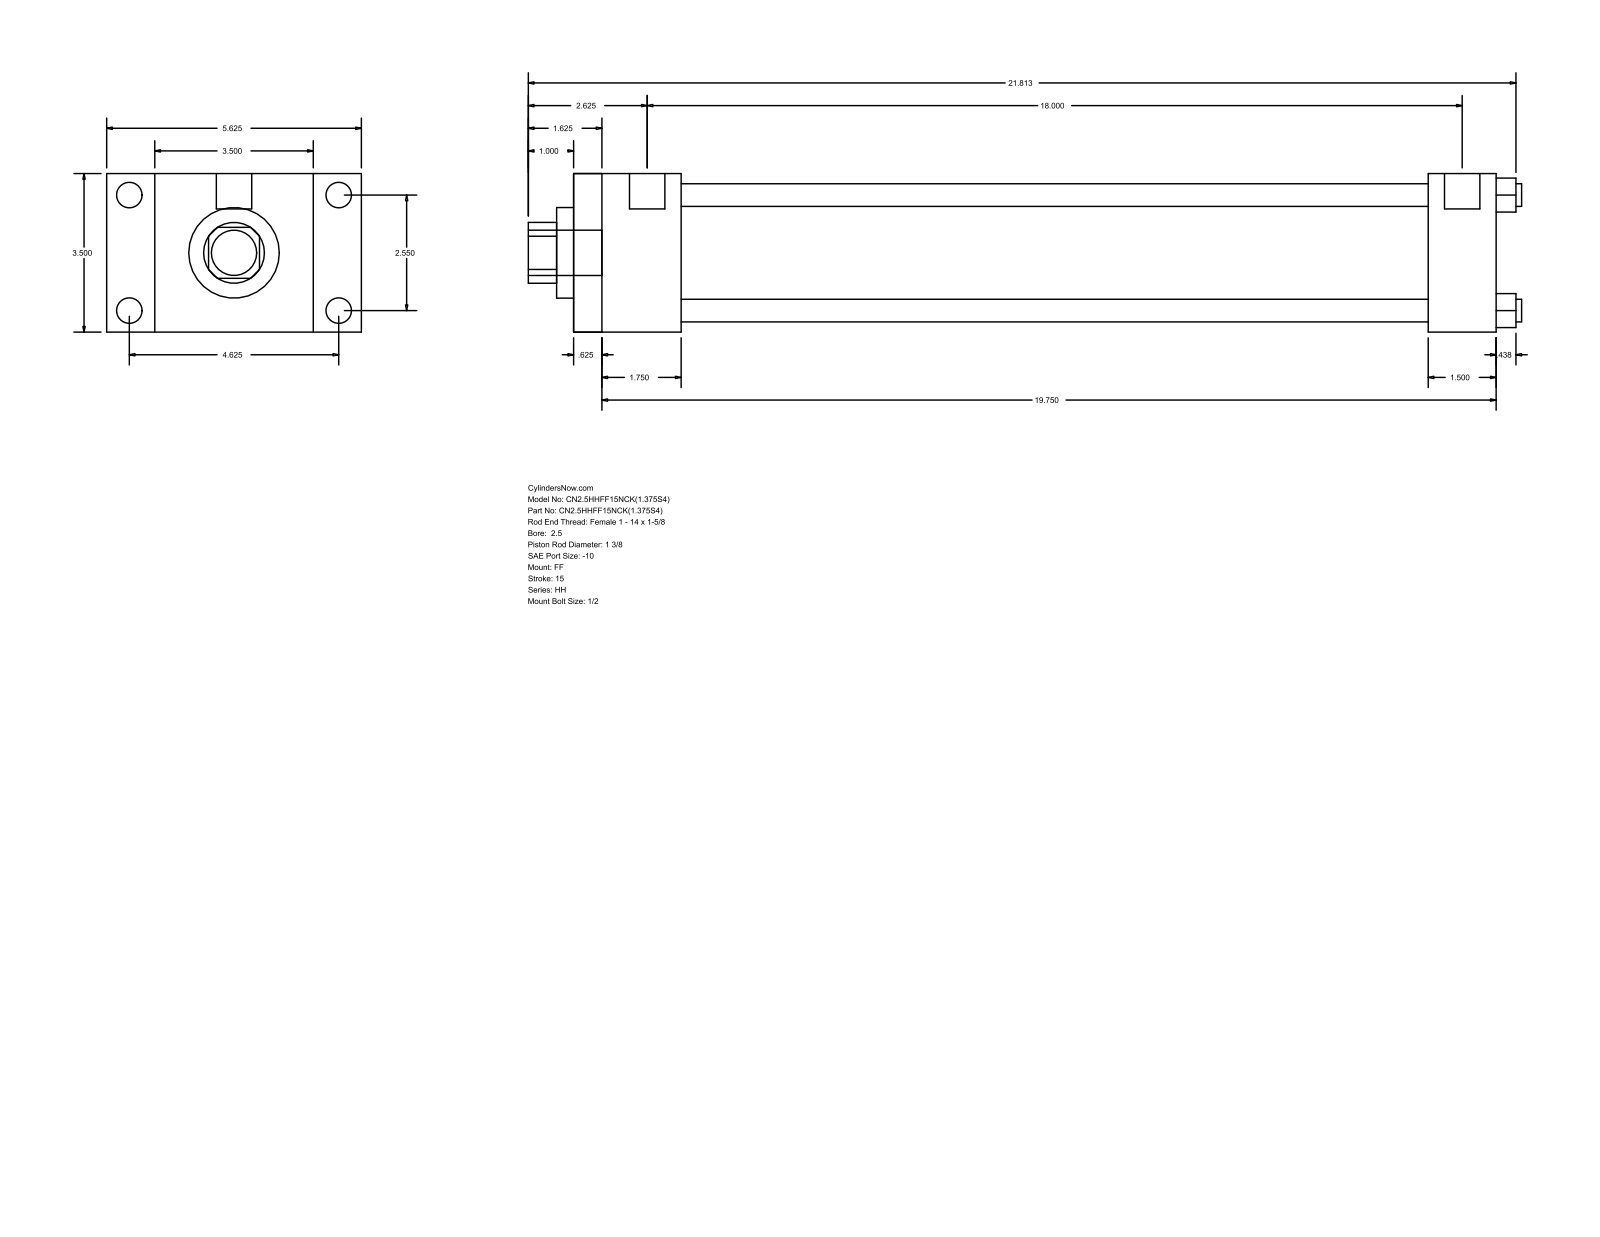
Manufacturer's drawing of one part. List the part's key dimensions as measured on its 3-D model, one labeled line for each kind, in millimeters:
Part name (STEP PRODUCT): HH_FF__0250_1.375
STEP written by: GSSL Pune (CONFIG_CONTROL_DESIGN)
Units: millimetres
Bodies: 0 solids, 92 faces (64 planar, 28 cylindrical, 0 other)
Overall size (bounding box): 557.21 × 142.88 × 88.9
Round holes (diameter × count): ⌀12.7 ×4, ⌀34.92 ×1, ⌀50.8 ×1, ⌀73.03 ×1
Round bosses / shafts (diameter × count): ⌀14.3 ×4, ⌀5.56 ×4, ⌀19.84 ×2, ⌀25.4 ×1
Partial cylindrical surfaces — rounded edges, fillets, slot ends (radius × count): R17.06 ×1
Main face-to-face distances: 88.9, 517.52, 15.87, 501.65, 60.32, 44.45, 457.2, 479.42, 463.55, 419.1
Hole centre spacings: 45.79, 64.76, 91.58
